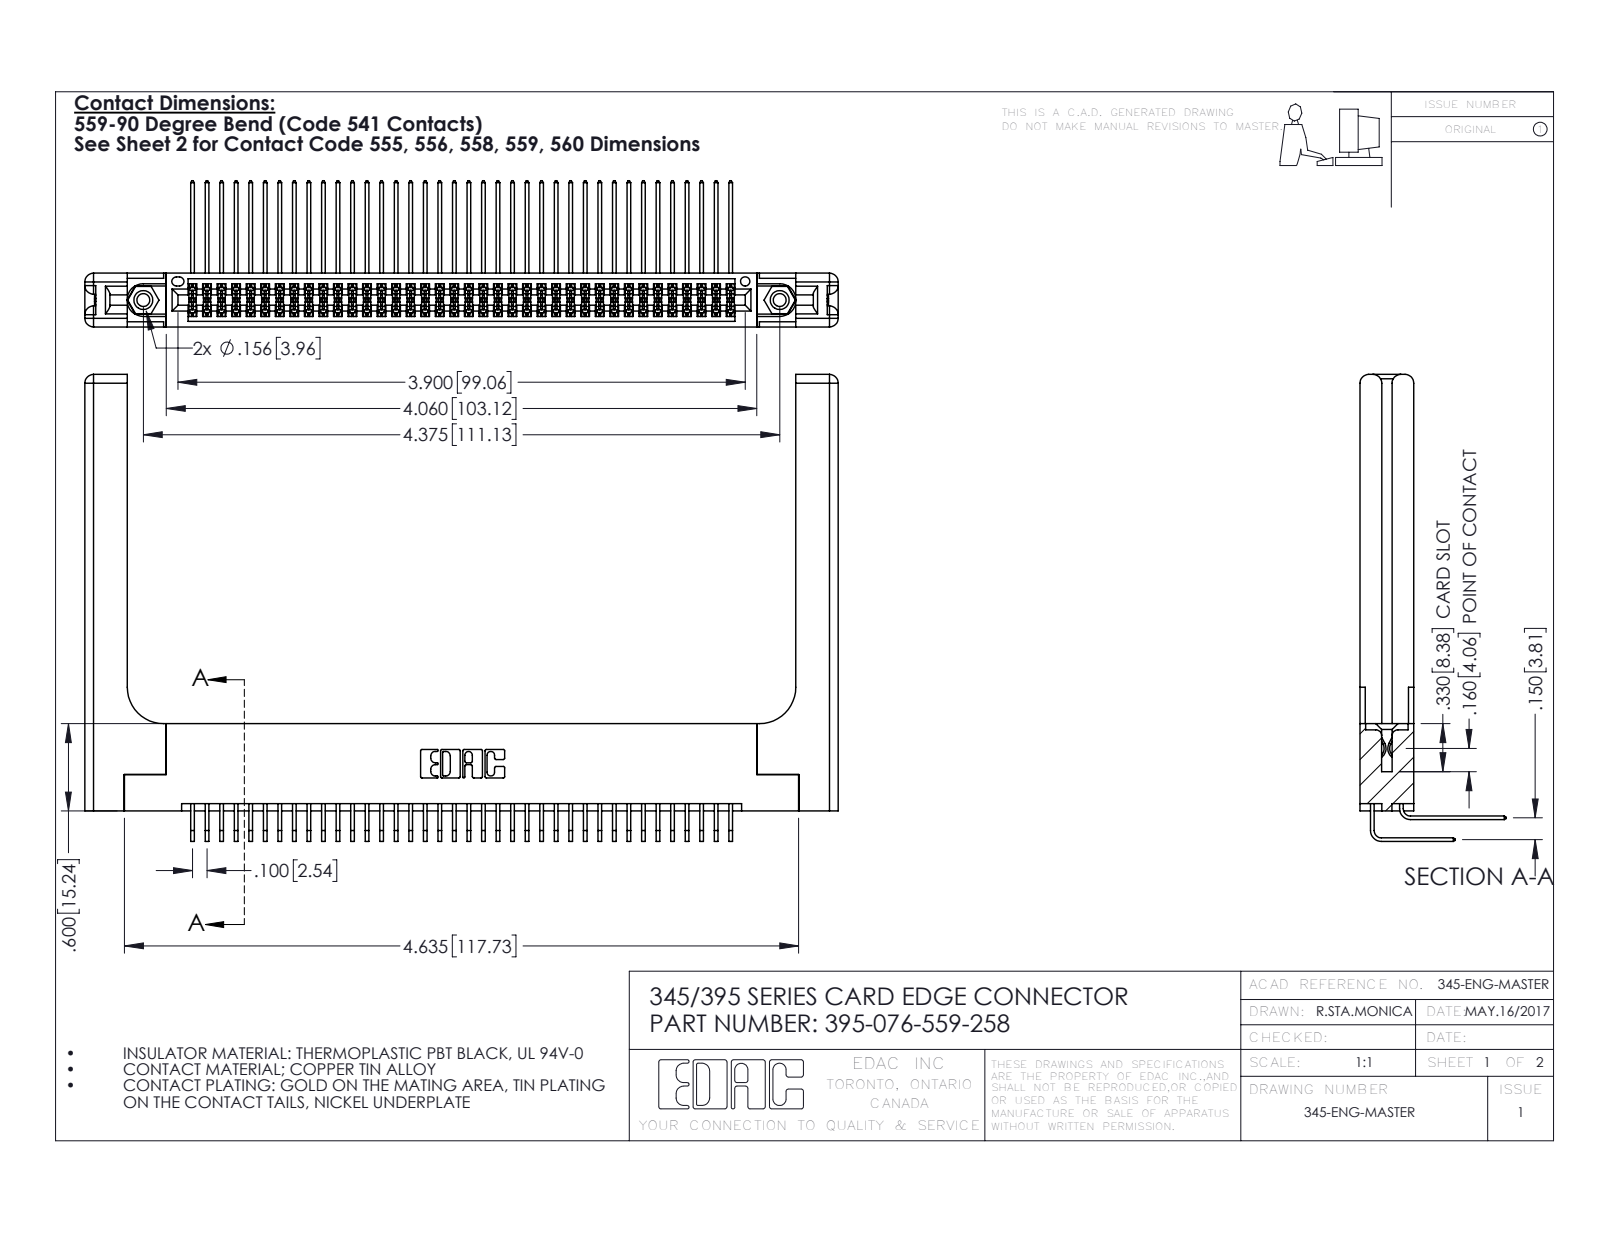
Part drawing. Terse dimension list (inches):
name: 345 Part_Flush Mounting Lugs - 0.156 Dia-TH; 345-292-001_558 559 Tail - 1; 345-292-001_559 Tail - 2; 345-220-058_345-220-058 (+2 more)
written by: SolidWorks 2016 (CONFIG_CONTROL_DESIGN)
unit: in
bodies: 81 solids, 4334 faces (2888 planar, 1386 cylindrical, 60 other)
size: 5.179 × 3.209 × 1.005
volume: 1.321 in³; area: 41.11 in²
holes: 2× ⌀0.089, 2× ⌀0.125, 2× ⌀0.156, 1× ⌀0.064
bosses: 2× ⌀0.155
rounds: 114× R0.006, 22× R0.01, 16× R0.06, 6× R0.007, 6× R0.031, 3× R0.026, 2× R0.014, 2× R0.019
face distances: 0.072, 0.37, 0.298, 0.2, 0.098, 0.272, 0.025, 0.225, 0.148, 0.15
hole spacings: 0.27, 4.139, 4.375
